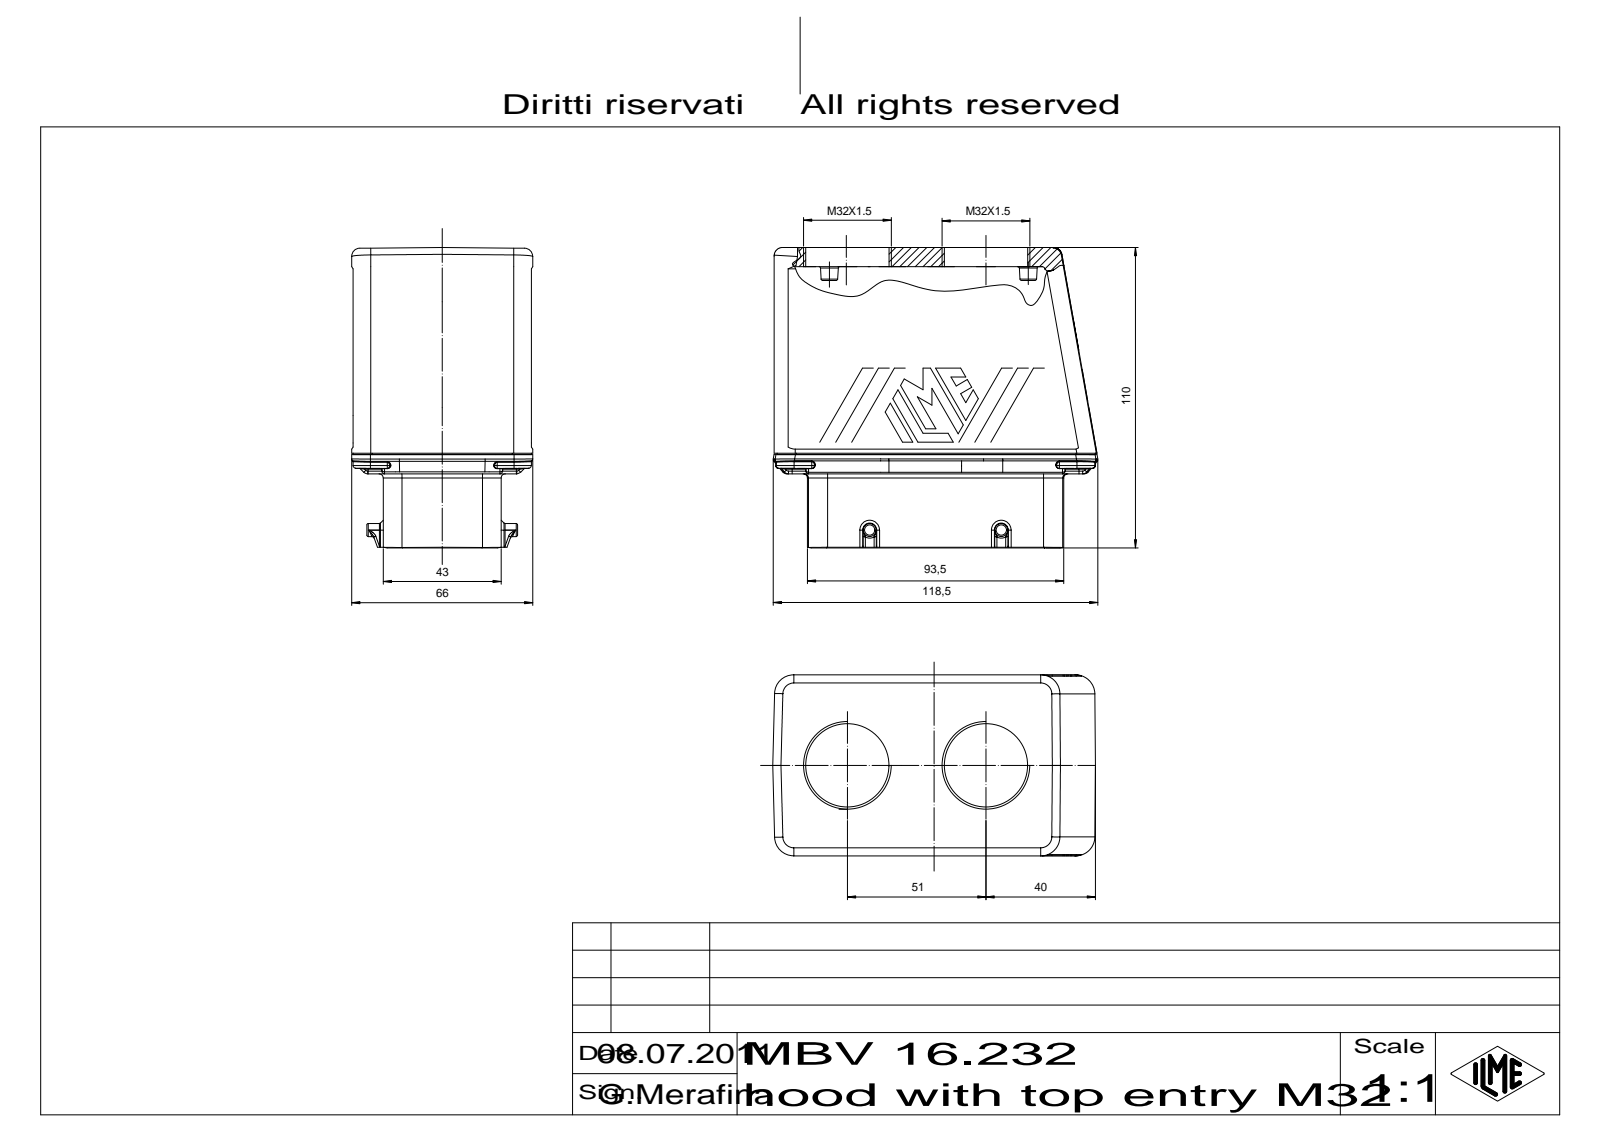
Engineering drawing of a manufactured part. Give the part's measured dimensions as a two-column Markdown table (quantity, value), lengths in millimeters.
| quantity | value |
| --- | --- |
| part name | 53848_Body_1 |
| STEP written by | CoCreate Modeling 16.00A 16-Aug-2008 (C) Parametric Technology GmbH (AUTOMOTIVE_DESIGN) |
| units | millimeters |
| bodies | 1 solid, 650 faces (334 planar, 152 cylindrical, 164 other) |
| overall size | 117.26 × 108.97 × 66.01 |
| volume | 571 203 mm³ |
| surface area | 61 939 mm² |
| round holes (diameter × count) | 32 × 2 |
| round bosses / shafts (diameter × count) | 4.8 × 2 |
| partial cylindrical surfaces (radius × count) | 1 × 44, 0.3 × 18, 7 × 12, 3 × 10, 0.5 × 8, 1.5 × 6, 4.2 × 4, 5 × 4 |
| main face-to-face distances | 65.01, 82.21, 0.4, 65.41, 11, 54.01, 54, 43, 11.01, 11.4 |
| hole center spacings | 50.53 |
